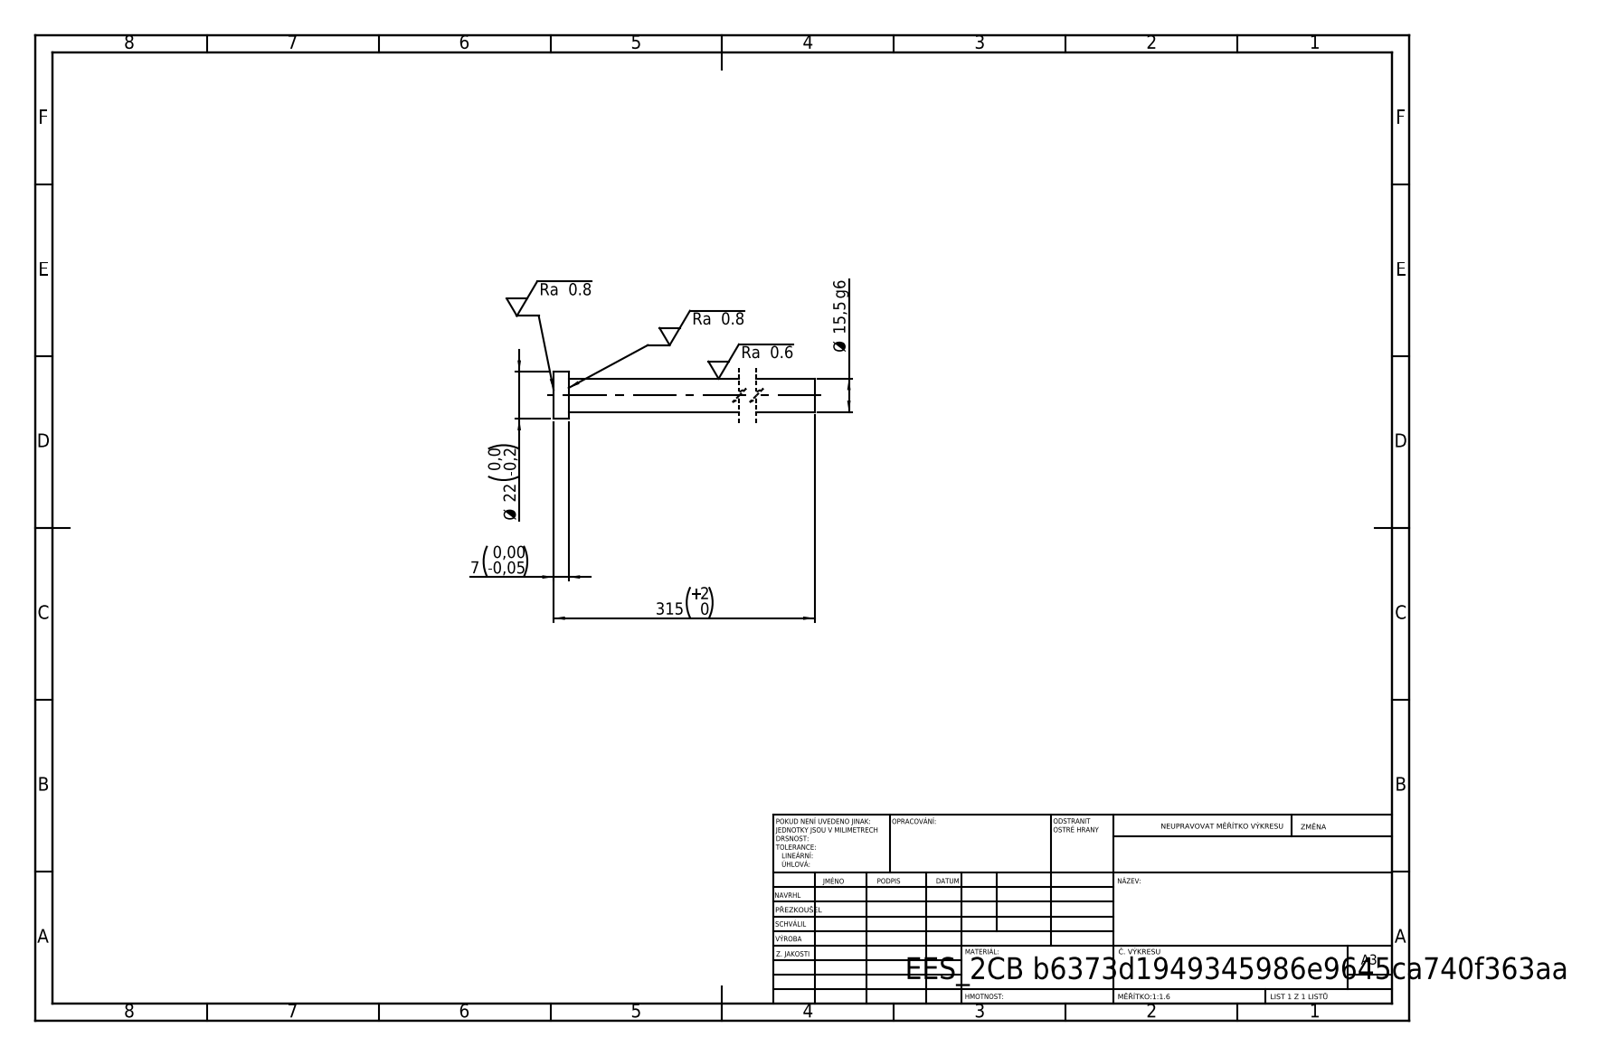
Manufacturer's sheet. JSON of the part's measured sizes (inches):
{"step_written_by": "SolidWorks 2019 (CONFIG_CONTROL_DESIGN)", "units": "inches", "bodies": {"solids": 1, "faces": 7, "planar": 3, "cylindrical": 4, "other": 0}, "overall_size": [12.402, 0.866, 0.866], "volume_in3": 3.709, "surface_area_in2": 25.18, "round_bosses_or_shafts": [[0.866, 1], [0.61, 1]], "face_to_face_distances": [0.276, 12.402, 12.126]}
